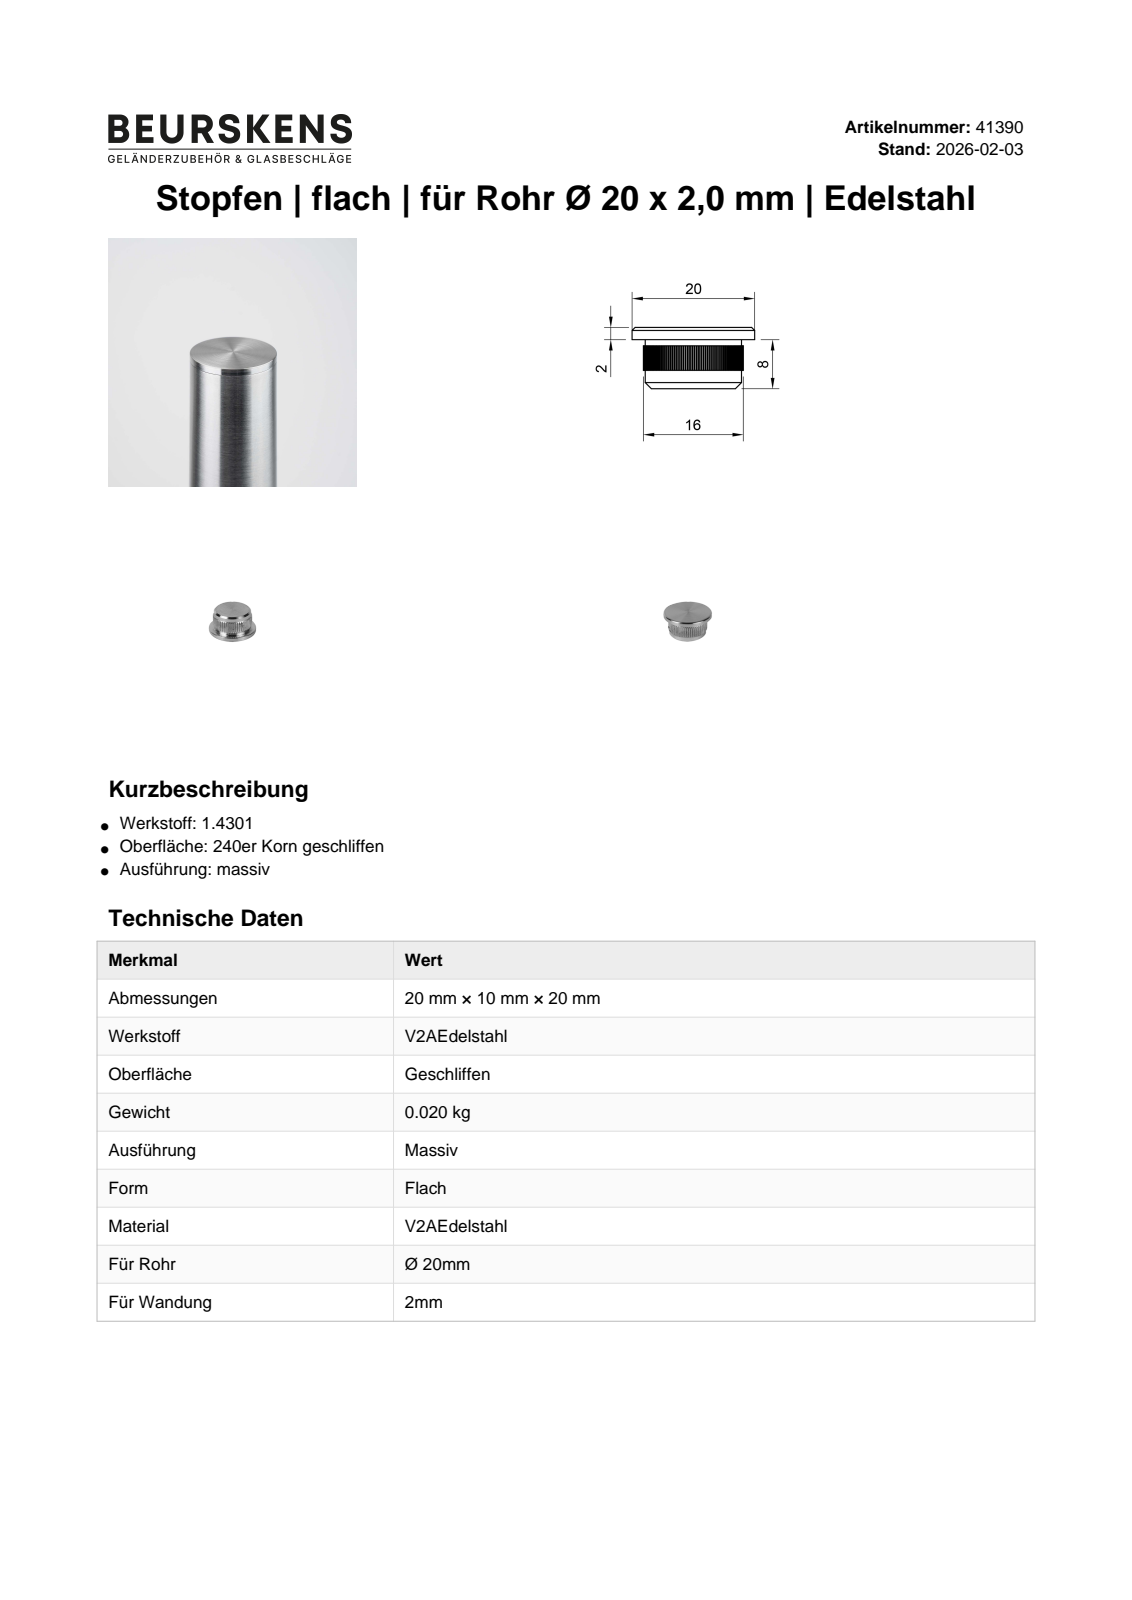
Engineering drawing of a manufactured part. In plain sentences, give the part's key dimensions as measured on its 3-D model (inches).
The part is named "41390". Its 3-D file was written by "Autodesk Inventor 2022 (AUTOMOTIVE_DESIGN)". It is 1 solid with 290 faces: 5 planar, 283 cylindrical and 2 other. Overall it measures 0.787 by 0.787 by 0.394 inches. Its volume is 0.134 cubic inches and its surface area 1.874 square inches. Round bosses or shafts: 1 of diameter 0.787, 1 of diameter 0.618. Partial cylindrical surfaces (rounded edges, fillets, slot ends): 140 of radius 0.005, 1 of radius 0.321. The main face-to-face distances are 0.394, 0.315, 0.079, 0.118, 0.276, 0.197, 0.157, 0.039.
